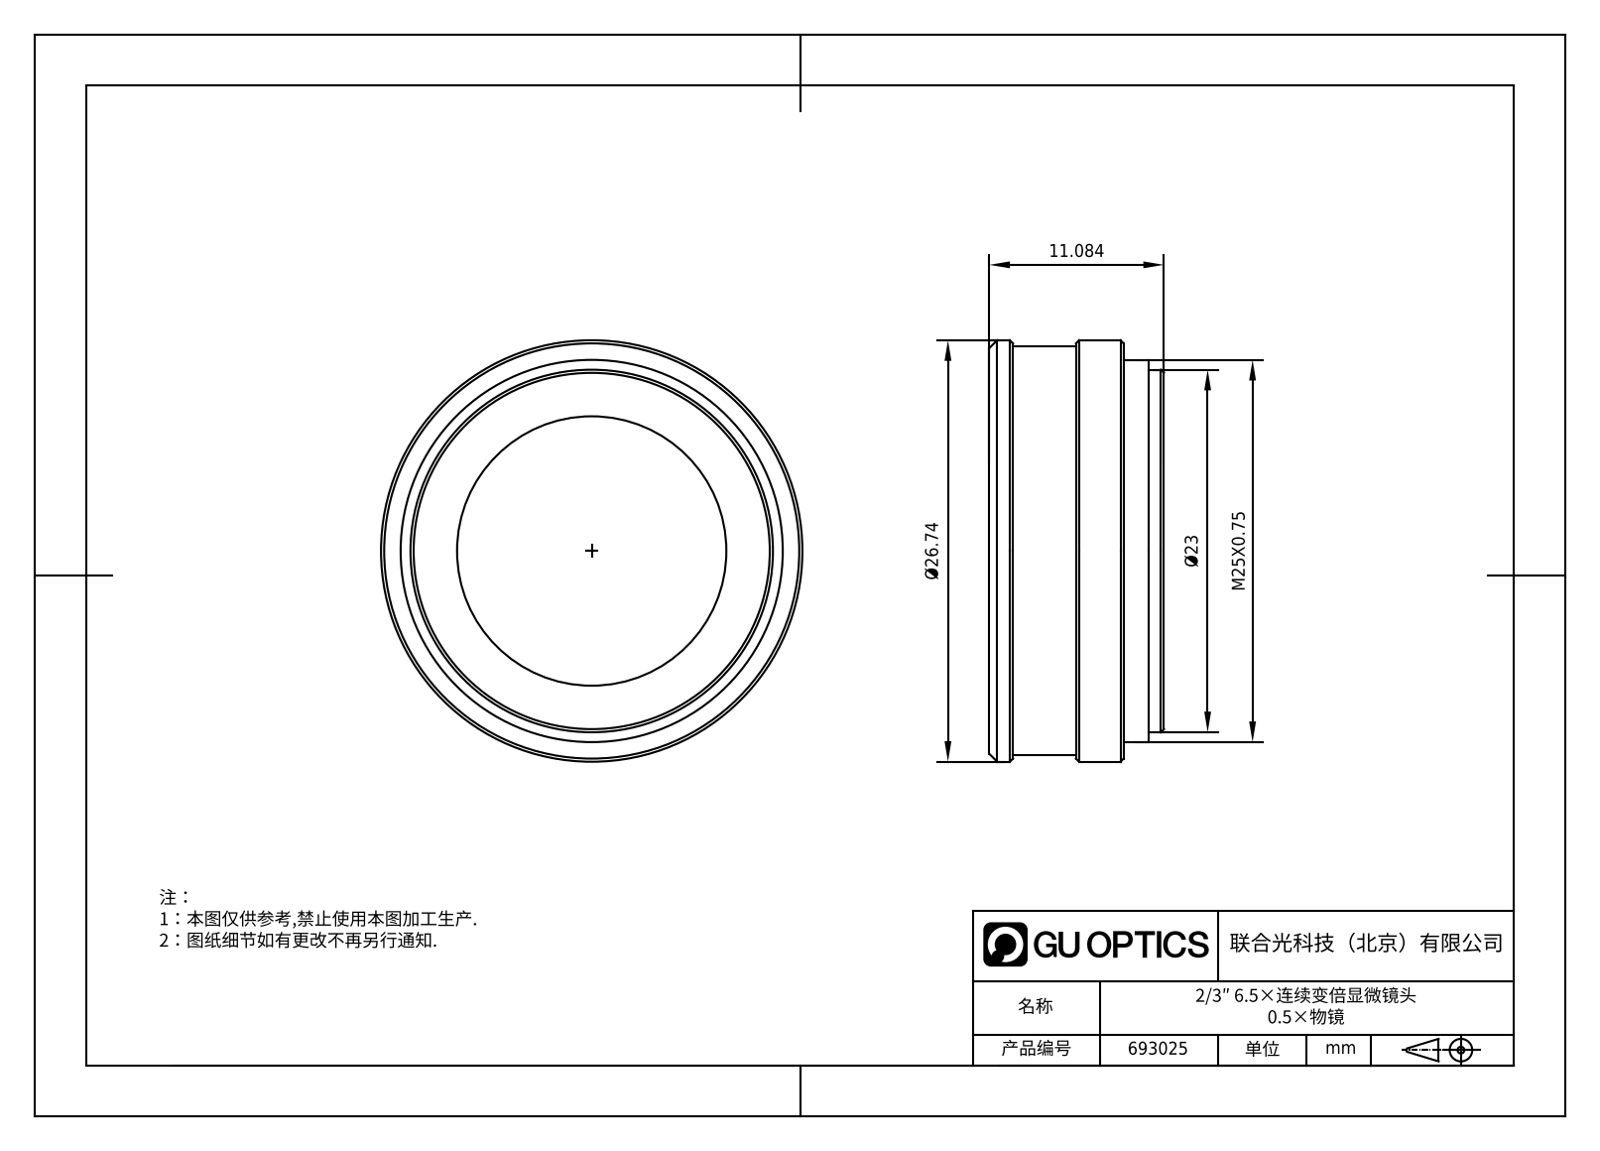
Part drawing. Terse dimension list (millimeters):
name: 66105
written by: SolidWorks 2015 (CONFIG_CONTROL_DESIGN)
unit: mm
bodies: 1 solid, 28 faces (6 planar, 12 cylindrical, 10 other)
size: 26.74 × 26.74 × 11.08
volume: 3 231 mm³; area: 2 160 mm²
holes: 1× ⌀17.09
bosses: 1× ⌀26.74, 1× ⌀25.94, 1× ⌀24.25, 1× ⌀23
face distances: 11.08, 8.52, 2.56, 10.08, 1.56, 1, 1.5, 7.02, 8.58, 9.58
